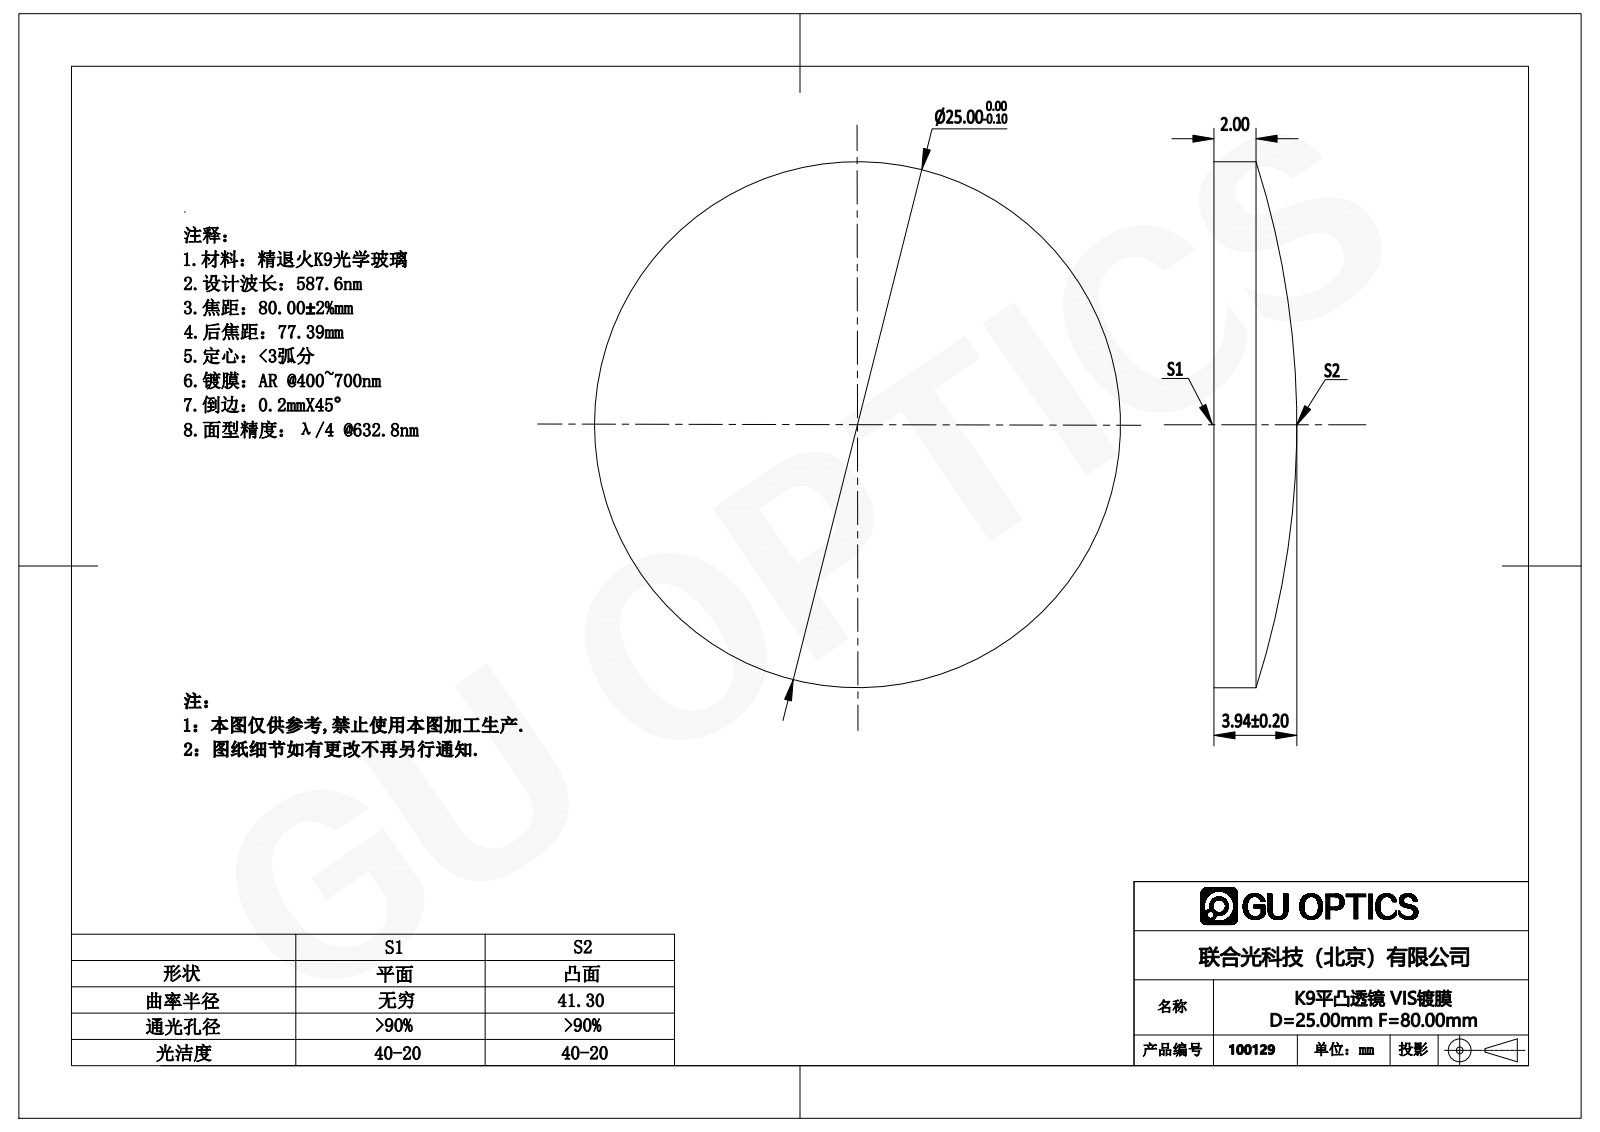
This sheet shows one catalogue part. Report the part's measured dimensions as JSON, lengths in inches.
{"part_name": "100129", "step_written_by": "SolidWorks 2016 (AUTOMOTIVE_DESIGN)", "units": "inches", "bodies": {"solids": 1, "faces": 5, "planar": 1, "cylindrical": 2, "other": 2}, "overall_size": [0.984, 0.984, 0.155], "volume_in3": 0.089, "surface_area_in2": 1.784, "round_bosses_or_shafts": [[0.984, 1]]}
